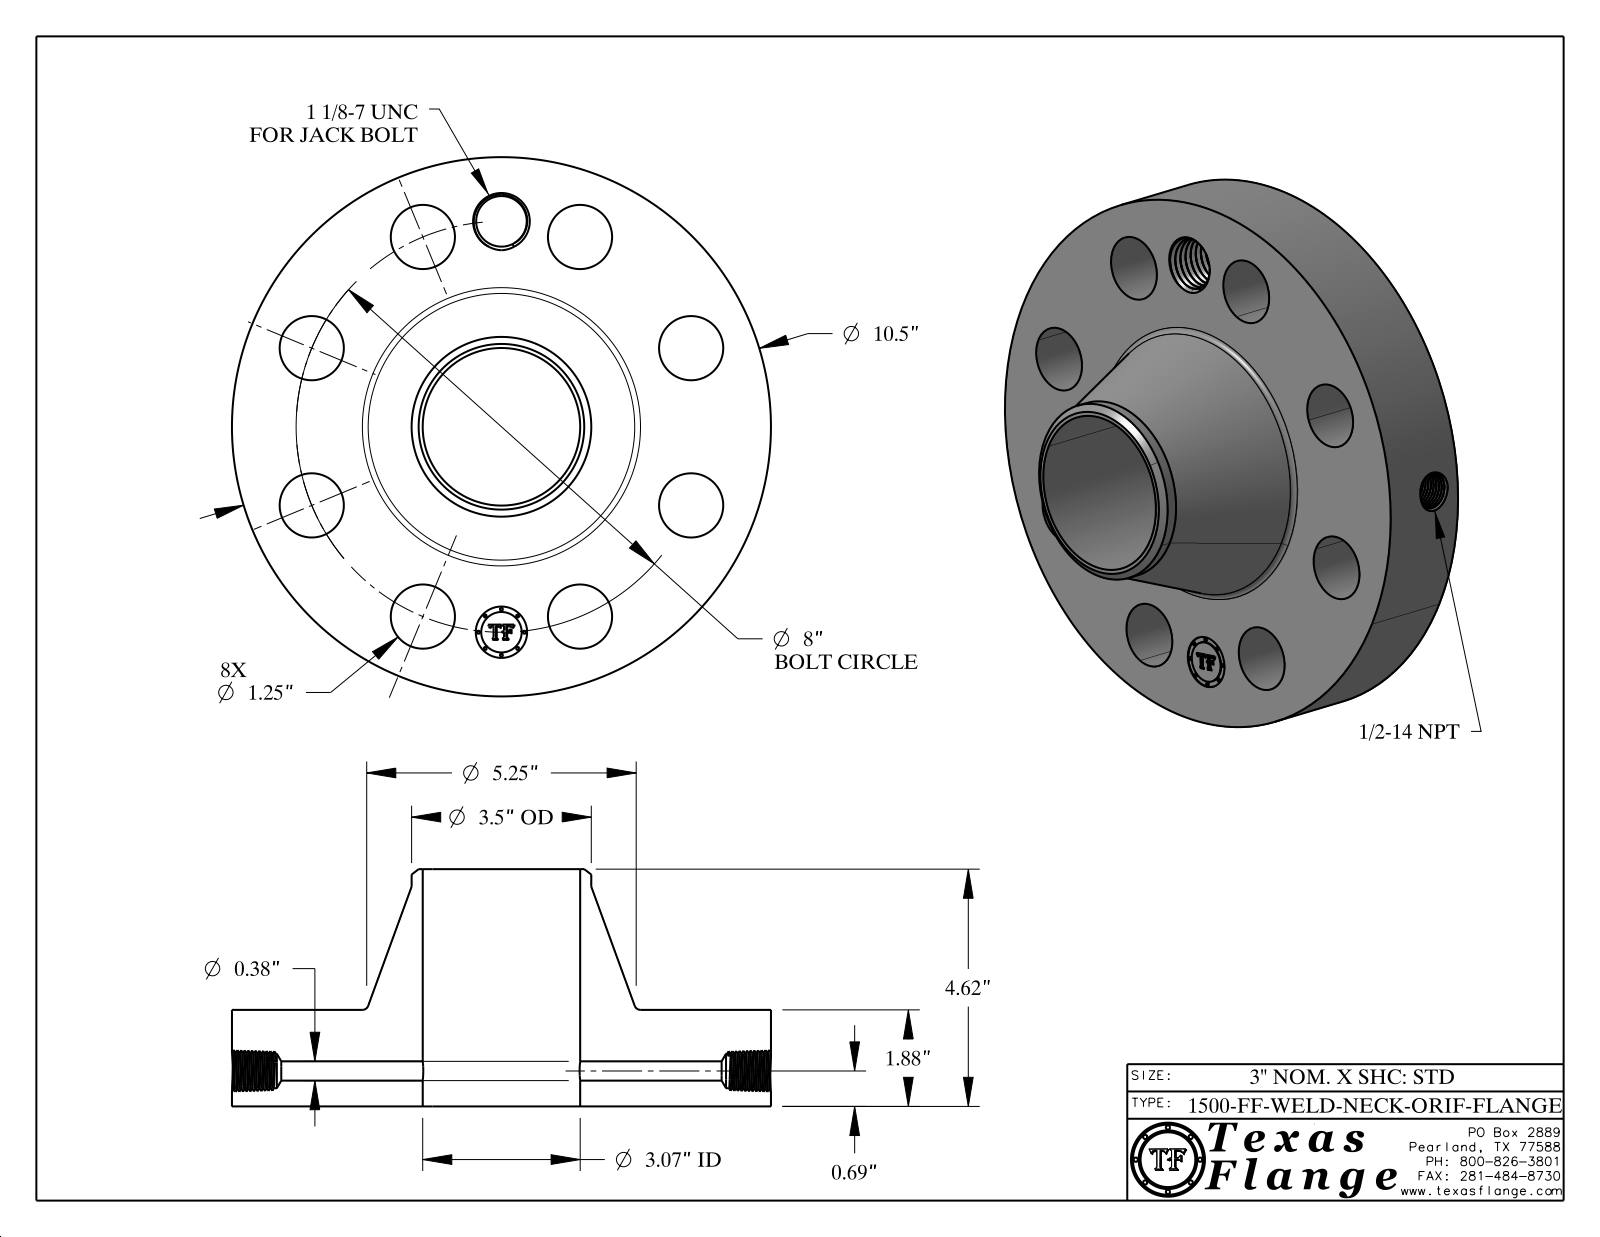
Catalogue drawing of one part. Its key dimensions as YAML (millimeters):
part_name: "1500-FF-WELD-NECK"
step_written_by: "CATIA V5 STEP AP214 (AUTOMOTIVE_DESIGN)"
units: millimeters
bodies: {solids: 1, faces: 757, planar: 368, cylindrical: 88, other: 301}
overall_size: [266.7, 266.7, 117.3]
volume: 2407000
surface_area: 226000
round_holes:
  - {diameter: 31.8, count: 8}
  - {diameter: 9.5, count: 1}
  - {diameter: 17.1, count: 1}
  - {diameter: 25, count: 1}
  - {diameter: 25.4, count: 1}
  - {diameter: 77.9, count: 1}
round_bosses_or_shafts:
  - {diameter: 1.5, count: 8}
  - {diameter: 266.7, count: 1}
  - {diameter: 88.9, count: 1}
  - {diameter: 20, count: 1}
face_to_face_distances: [47.8, 117.3, 69.6, 47.4, 0.4, 70, 7.6, 7.4, 1.4, 6.3]
hole_center_spacings: [101.6, 143.7, 187.7, 39.6, 77.7, 77.8, 112.9, 169]
